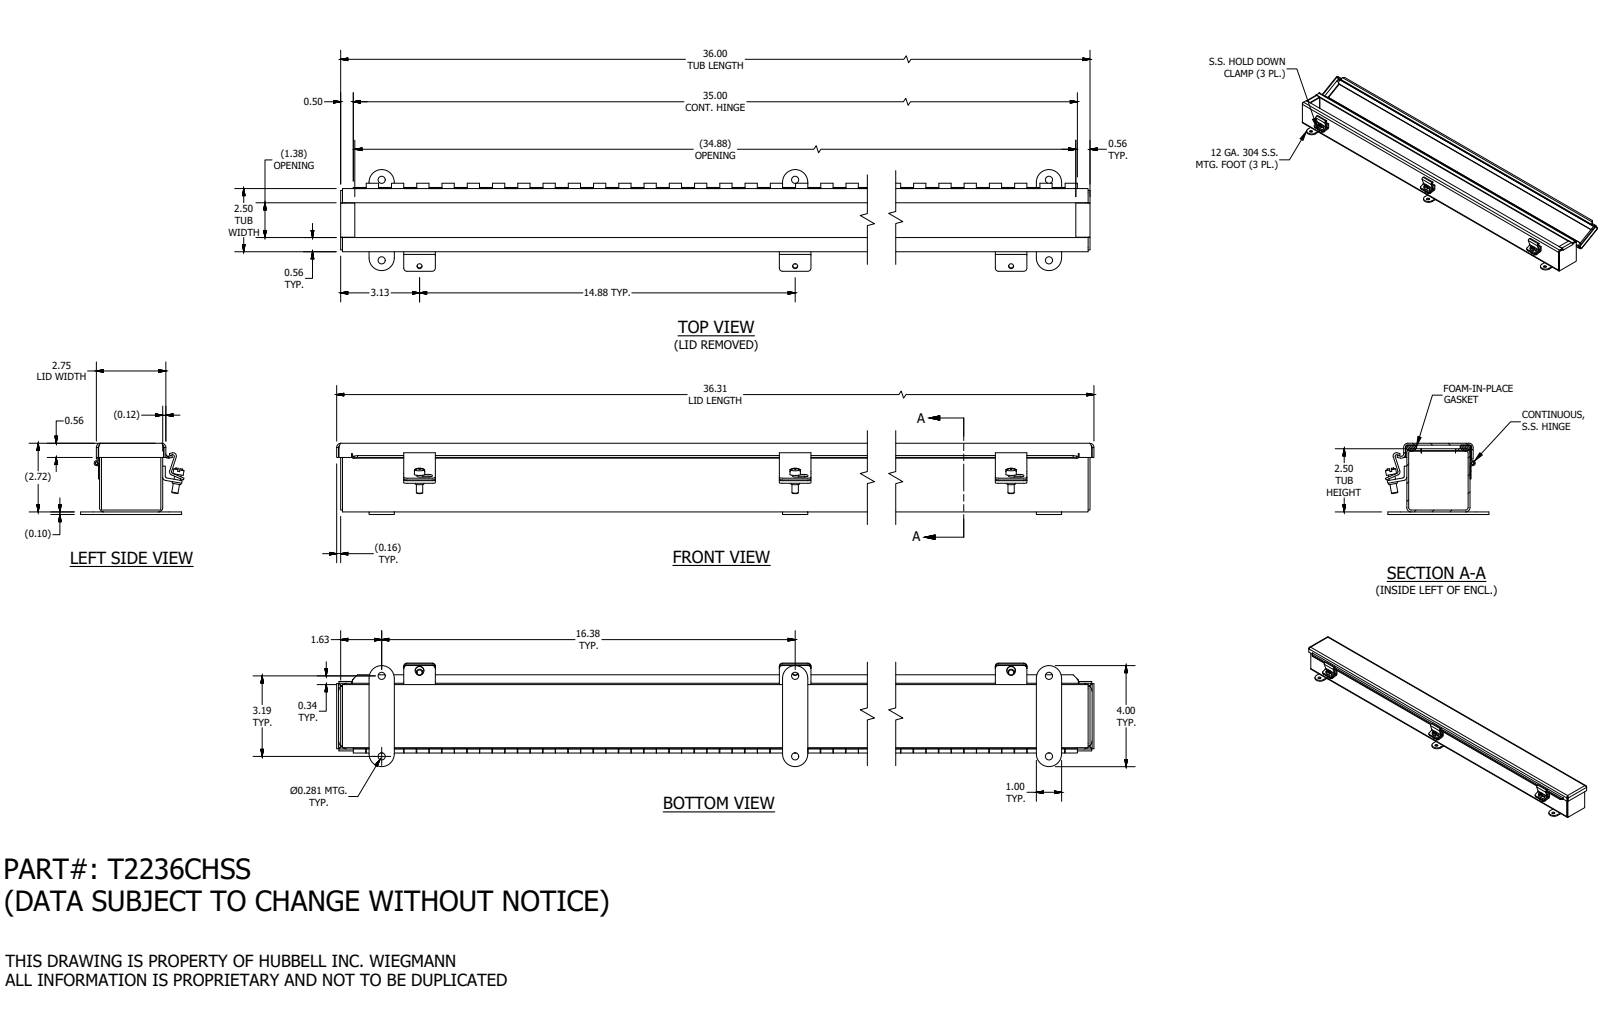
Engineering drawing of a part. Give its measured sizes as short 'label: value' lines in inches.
name: T2236CHSS
written by: SolidWorks 2019 (AUTOMOTIVE_DESIGN)
unit: in
bodies: 20 solids, 719 faces (431 planar, 249 cylindrical, 39 other)
size: 36.313 × 4.098 × 2.822
volume: 44.32 in³; area: 1 173 in²
holes: 6× ⌀0.11, 6× ⌀0.281, 3× ⌀0.196, 1× ⌀0.116
bosses: 3× ⌀0.41, 3× ⌀0.344, 3× ⌀0.25, 1× ⌀0.2, 1× ⌀0.1
rounds: 12× R0.125, 11× R0.094, 11× R0.168, 8× R0.085, 6× R0.133, 6× R0.5, 4× R0.242, 3× R0.063
face distances: 0.074, 2.426, 2.644, 2.5, 2.352, 2.718, 2.57, 0.218, 2.552, 0.126
hole spacings: 14.875, 16.375, 16.682, 0.75, 3.187, 14.875, 29.75, 32.75
